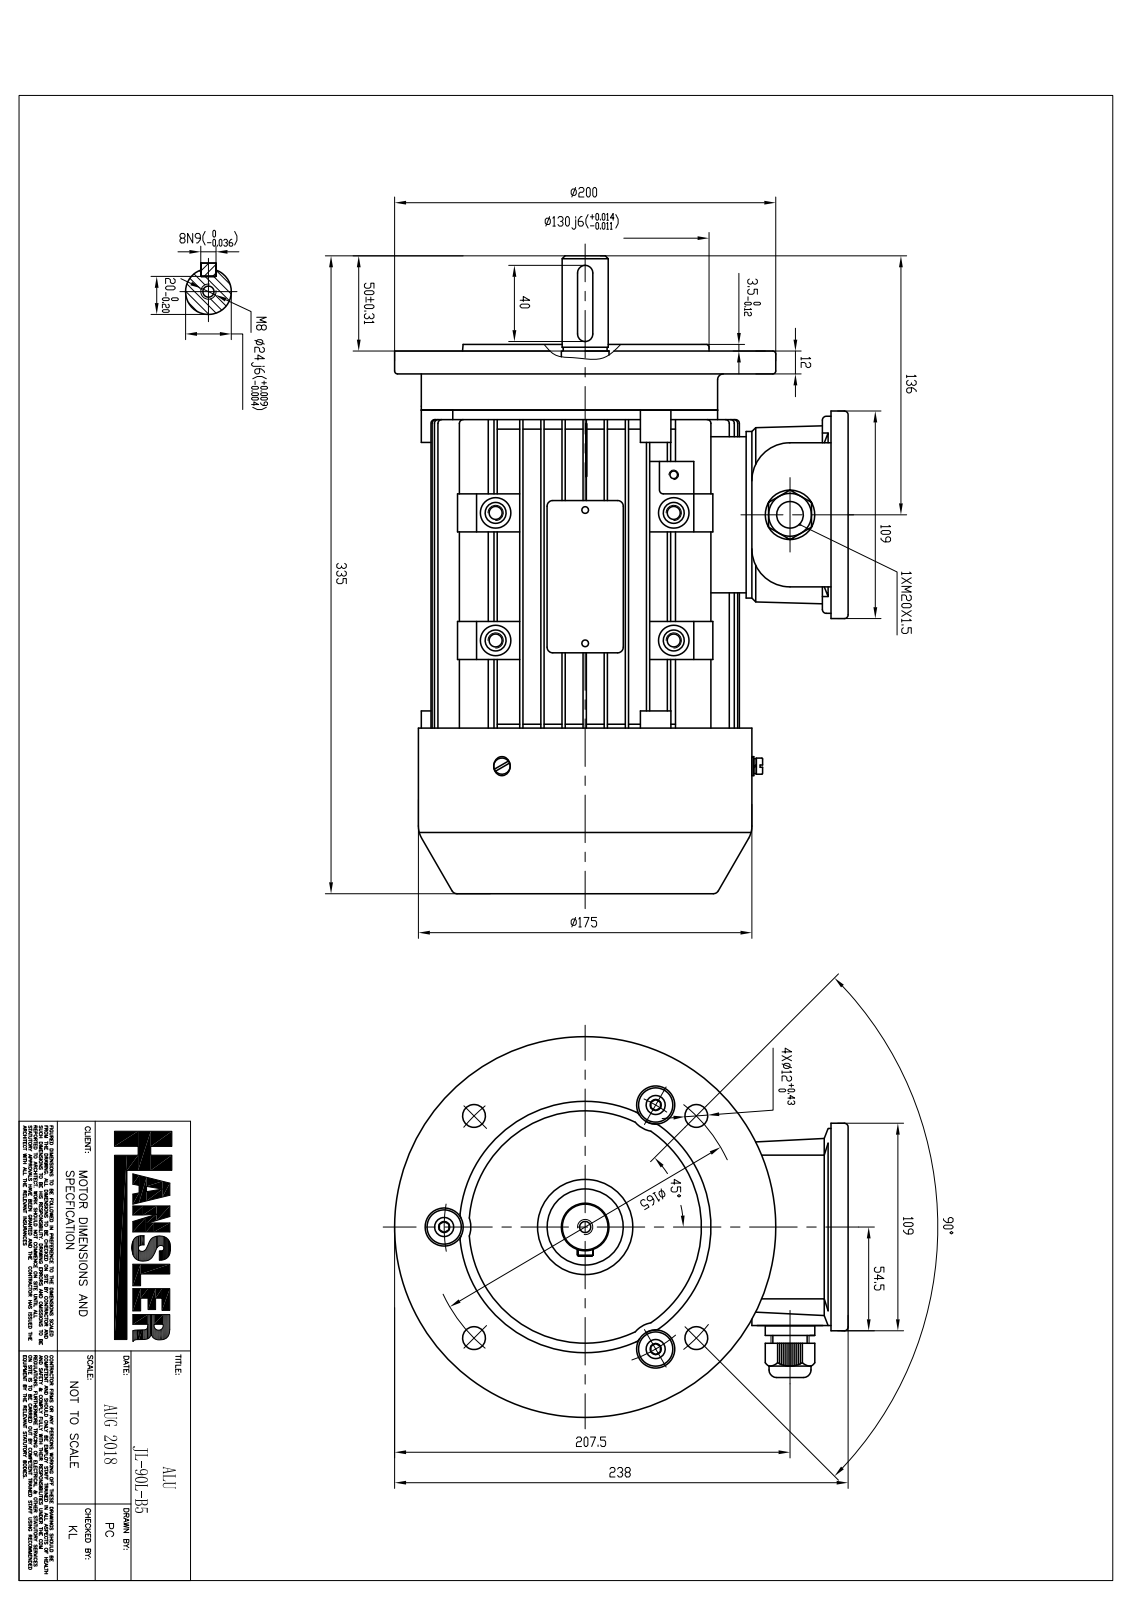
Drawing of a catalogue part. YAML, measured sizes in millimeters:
part_name: "JL-90L-B5"
step_written_by: "SIEMENS PLM Software NX 12.0 (AP203_CONFIGURATION_CONTROLLED_3D_DESIGN_OF_MECHANICAL_PARTS_AND_ASSEMBLIES_MIM_LF)"
units: millimeters
bodies: {solids: 41, faces: 3987, planar: 2432, cylindrical: 1172, other: 383}
overall_size: [335, 240.5, 200]
volume: 1404000
surface_area: 873577
round_holes:
  - {diameter: 4, count: 13}
  - {diameter: 5, count: 11}
  - {diameter: 5.8, count: 10}
  - {diameter: 8, count: 10}
  - {diameter: 16, count: 8}
  - {diameter: 4.8, count: 4}
  - {diameter: 5.25, count: 4}
  - {diameter: 5.3, count: 4}
  - {diameter: 12, count: 4}
  - {diameter: 6, count: 3}
  - {diameter: 6.39, count: 3}
  - {diameter: 7, count: 3}
round_bosses_or_shafts:
  - {diameter: 11, count: 8}
  - {diameter: 4.48, count: 8}
  - {diameter: 10, count: 7}
  - {diameter: 12, count: 4}
  - {diameter: 7.85, count: 4}
  - {diameter: 5, count: 4}
  - {diameter: 9.59, count: 3}
  - {diameter: 5.35, count: 3}
partial_cylinders:
  - {radius: 0.5, count: 464}
  - {radius: 2, count: 69}
  - {radius: 3, count: 31}
  - {radius: 4, count: 19}
  - {radius: 0.75, count: 16}
  - {radius: 5, count: 8}
  - {radius: 7, count: 8}
  - {radius: 2.5, count: 6}
face_to_face_distances: [1.7, 11.08, 44.32, 22.16, 5, 2.5, 55.4, 9.38, 12.78, 33.24]
hole_center_spacings: [35.51, 50.8, 57.1, 72.54, 77.07, 22, 15, 15.56]
